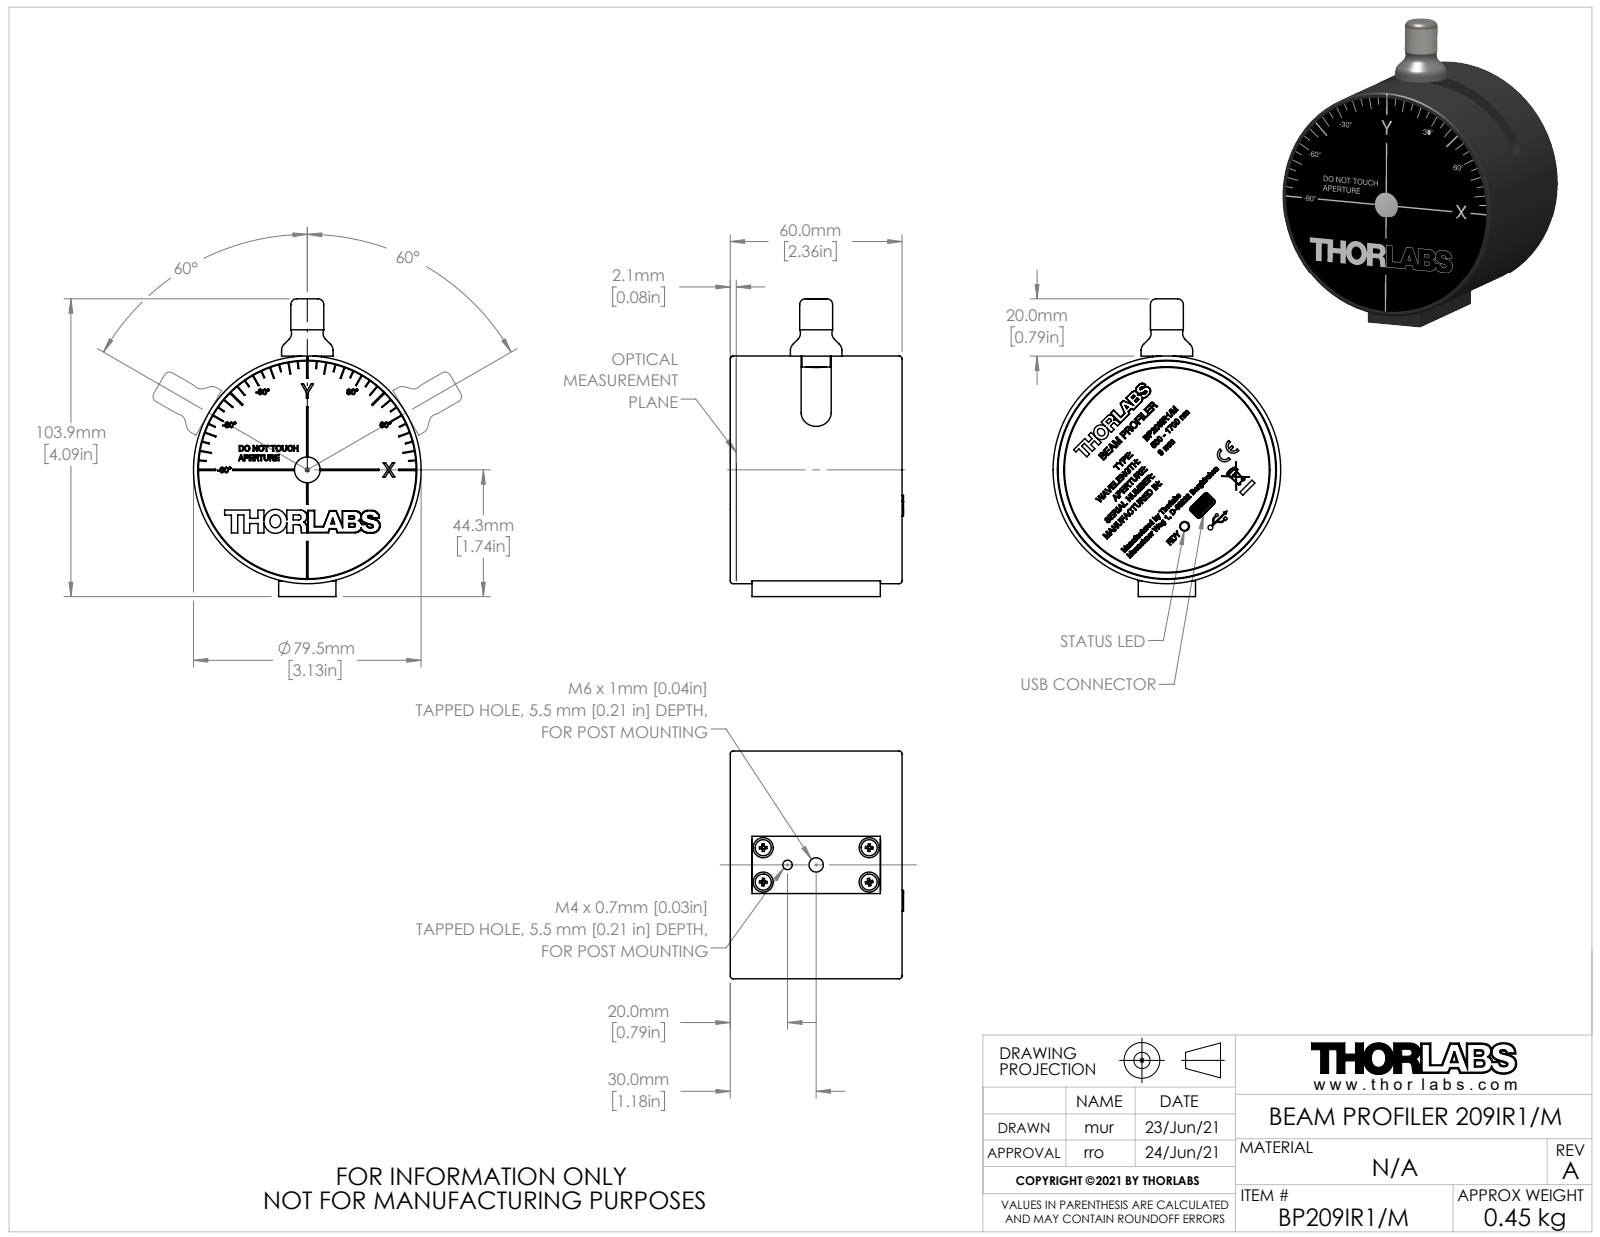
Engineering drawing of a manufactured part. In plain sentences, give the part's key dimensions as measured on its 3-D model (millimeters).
The part is named "22.02.10_BP209IR1_M WEB". Its 3-D file was written by "SolidWorks 2019 (AUTOMOTIVE_DESIGN)". It is 14 solids with 4612 faces: 3223 planar, 284 cylindrical and 1105 other. Overall it measures 103.95 by 79.5 by 60.5 millimeters. Its volume is 98 403 cubic millimeters and its surface area 99 234 square millimeters. Round holes: 10 of diameter 3.2, 9 of diameter 2.2, 8 of diameter 8, 6 of diameter 1.6, 6 of diameter 6.3, 5 of diameter 5, 5 of diameter 7, 4 of diameter 2.5, 4 of diameter 5.3, 1 of diameter 1, 1 of diameter 1.29, 1 of diameter 1.67. Round bosses or shafts: 4 of diameter 5.6, 4 of diameter 3, 2 of diameter 0.8, 1 of diameter 79.5, 1 of diameter 76, 1 of diameter 72.1, 1 of diameter 71.8, 1 of diameter 71.5. Partial cylindrical surfaces (rounded edges, fillets, slot ends): 18 of radius 1.5, 16 of radius 4, 14 of radius 0.1, 14 of radius 0.2, 14 of radius 1, 9 of radius 0.3, 8 of radius 0.7, 8 of radius 5. The main face-to-face distances are 1, 59, 59.7, 60, 58, 0.7, 58.7, 0.5, 2, 1.5. The hole center spacings are 23.73, 31, 43.84, 57.28, 27, 46.77, 27.01, 19.45.
